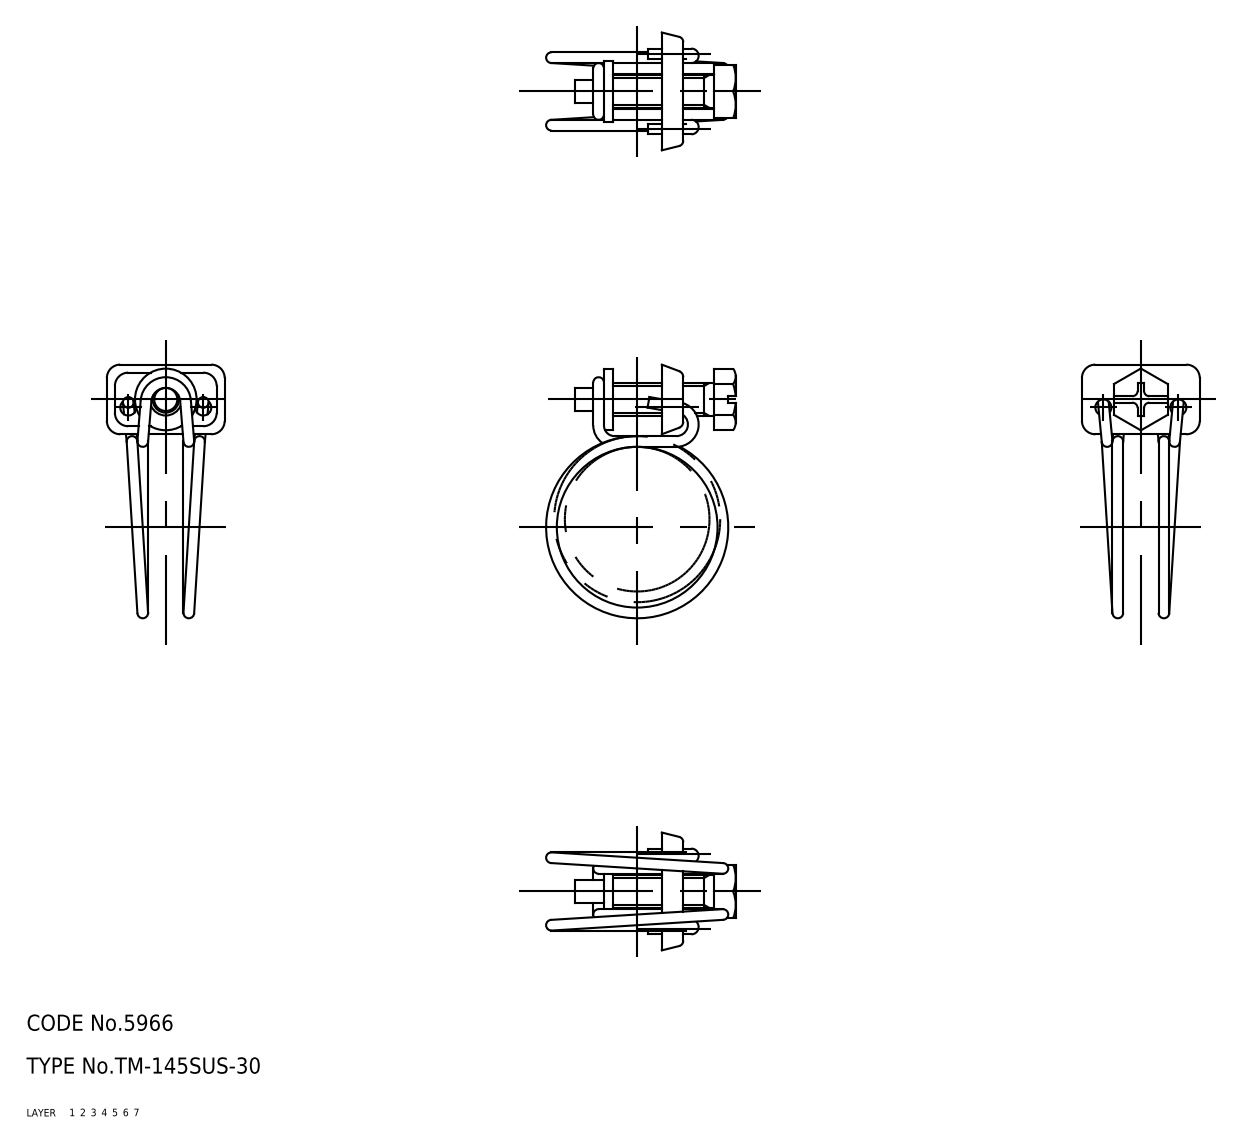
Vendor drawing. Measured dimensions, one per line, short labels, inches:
name: screw; holder; band; TM_145SUS_30_21919_36
written by: CADfix (AUTOMOTIVE_DESIGN)
unit: in
bodies: 3 solids, 119 faces (0 planar, 0 cylindrical, 119 other)
size: 1.864 × 1.394 × 0.866
volume: 0.152 in³; area: 5.565 in²
